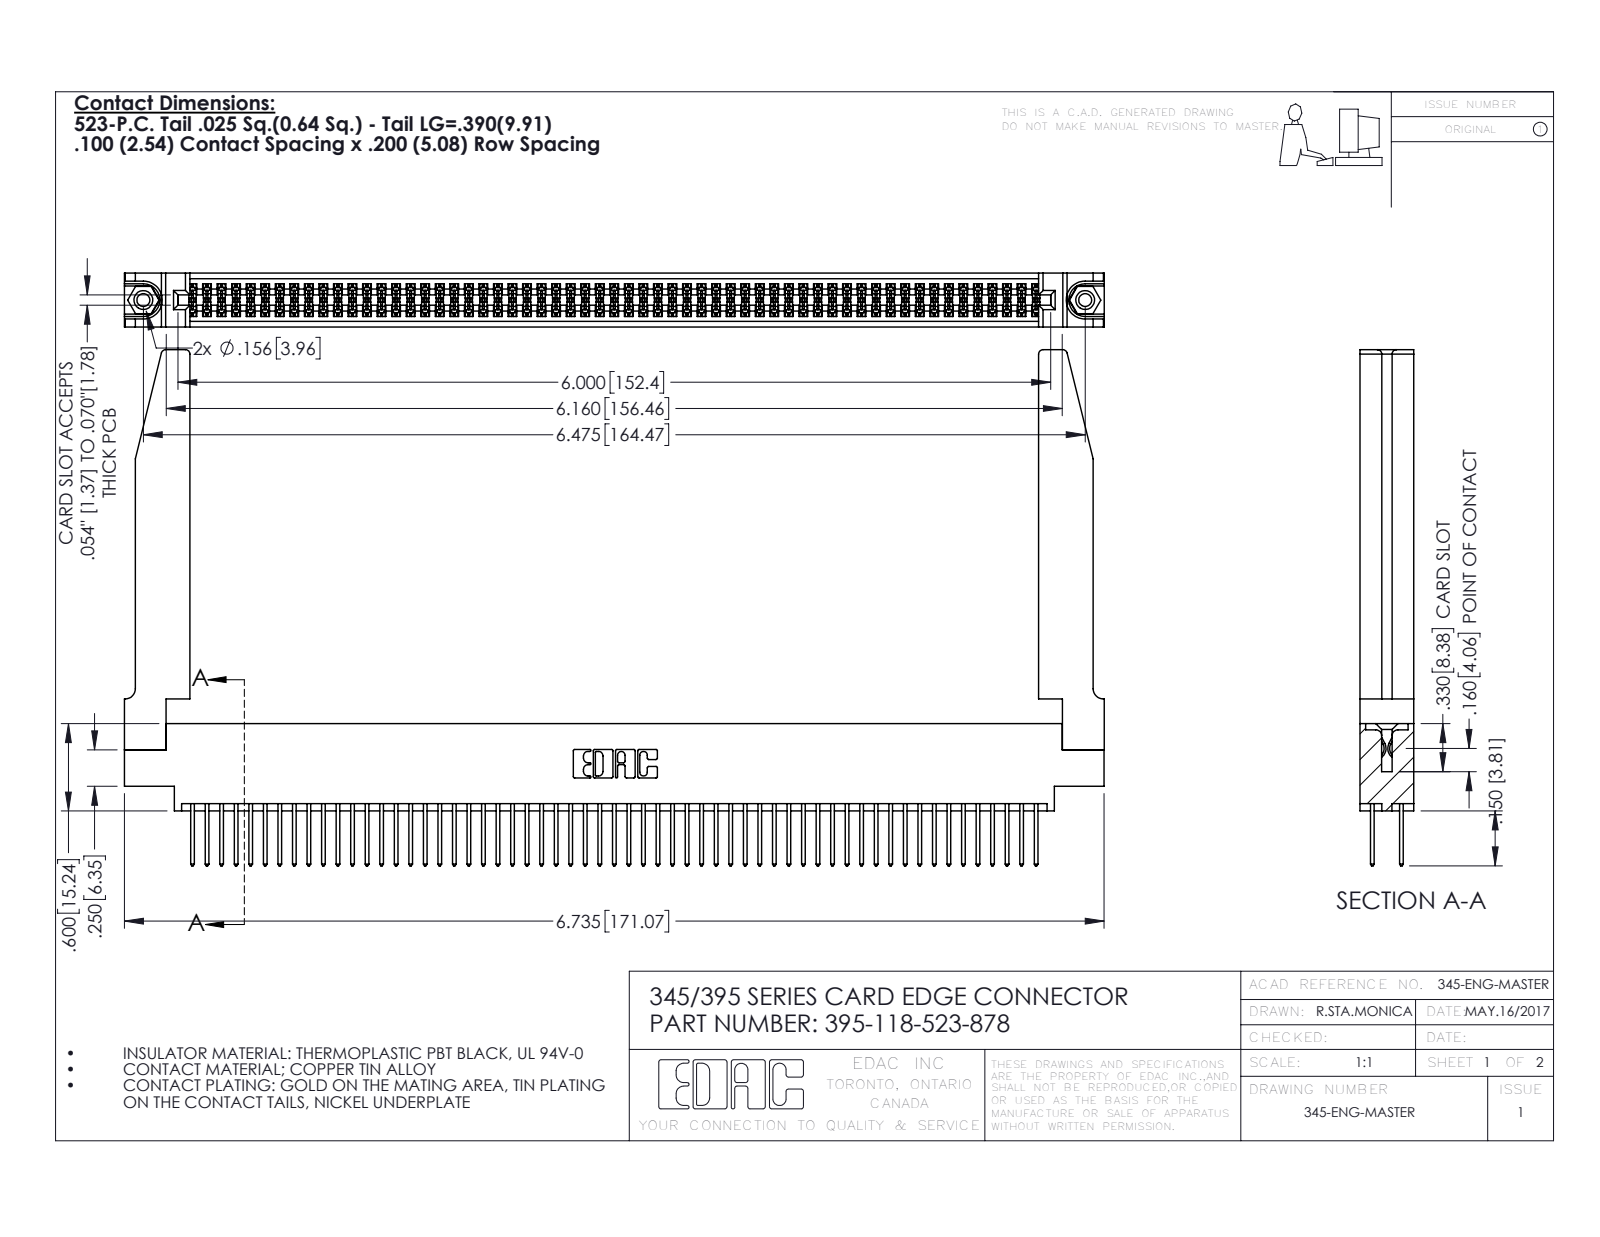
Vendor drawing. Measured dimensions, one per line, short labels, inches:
name: 345 Part_0.170 Offset - 0.156 Dia-TH; 345-250-001_345-250-001-102; 345-220-078_345-220-078; 395-118-523-878 (+1 more)
written by: SolidWorks 2016 (CONFIG_CONTROL_DESIGN)
unit: in
bodies: 123 solids, 6264 faces (4120 planar, 2092 cylindrical, 52 other)
size: 6.736 × 3.547 × 0.37
volume: 1.506 in³; area: 51.75 in²
holes: 2× ⌀0.089, 2× ⌀0.125, 2× ⌀0.156, 1× ⌀0.064
bosses: 2× ⌀0.155
rounds: 177× R0.006, 118× R0.01, 22× R0.01, 8× R0.03, 6× R0.007, 6× R0.031, 3× R0.026, 2× R0.014
face distances: 0.072, 0.298, 0.37, 0.098, 0.272, 0.025, 0.2, 0.225, 0.175, 0.148
hole spacings: 0.27, 6.239, 6.475
